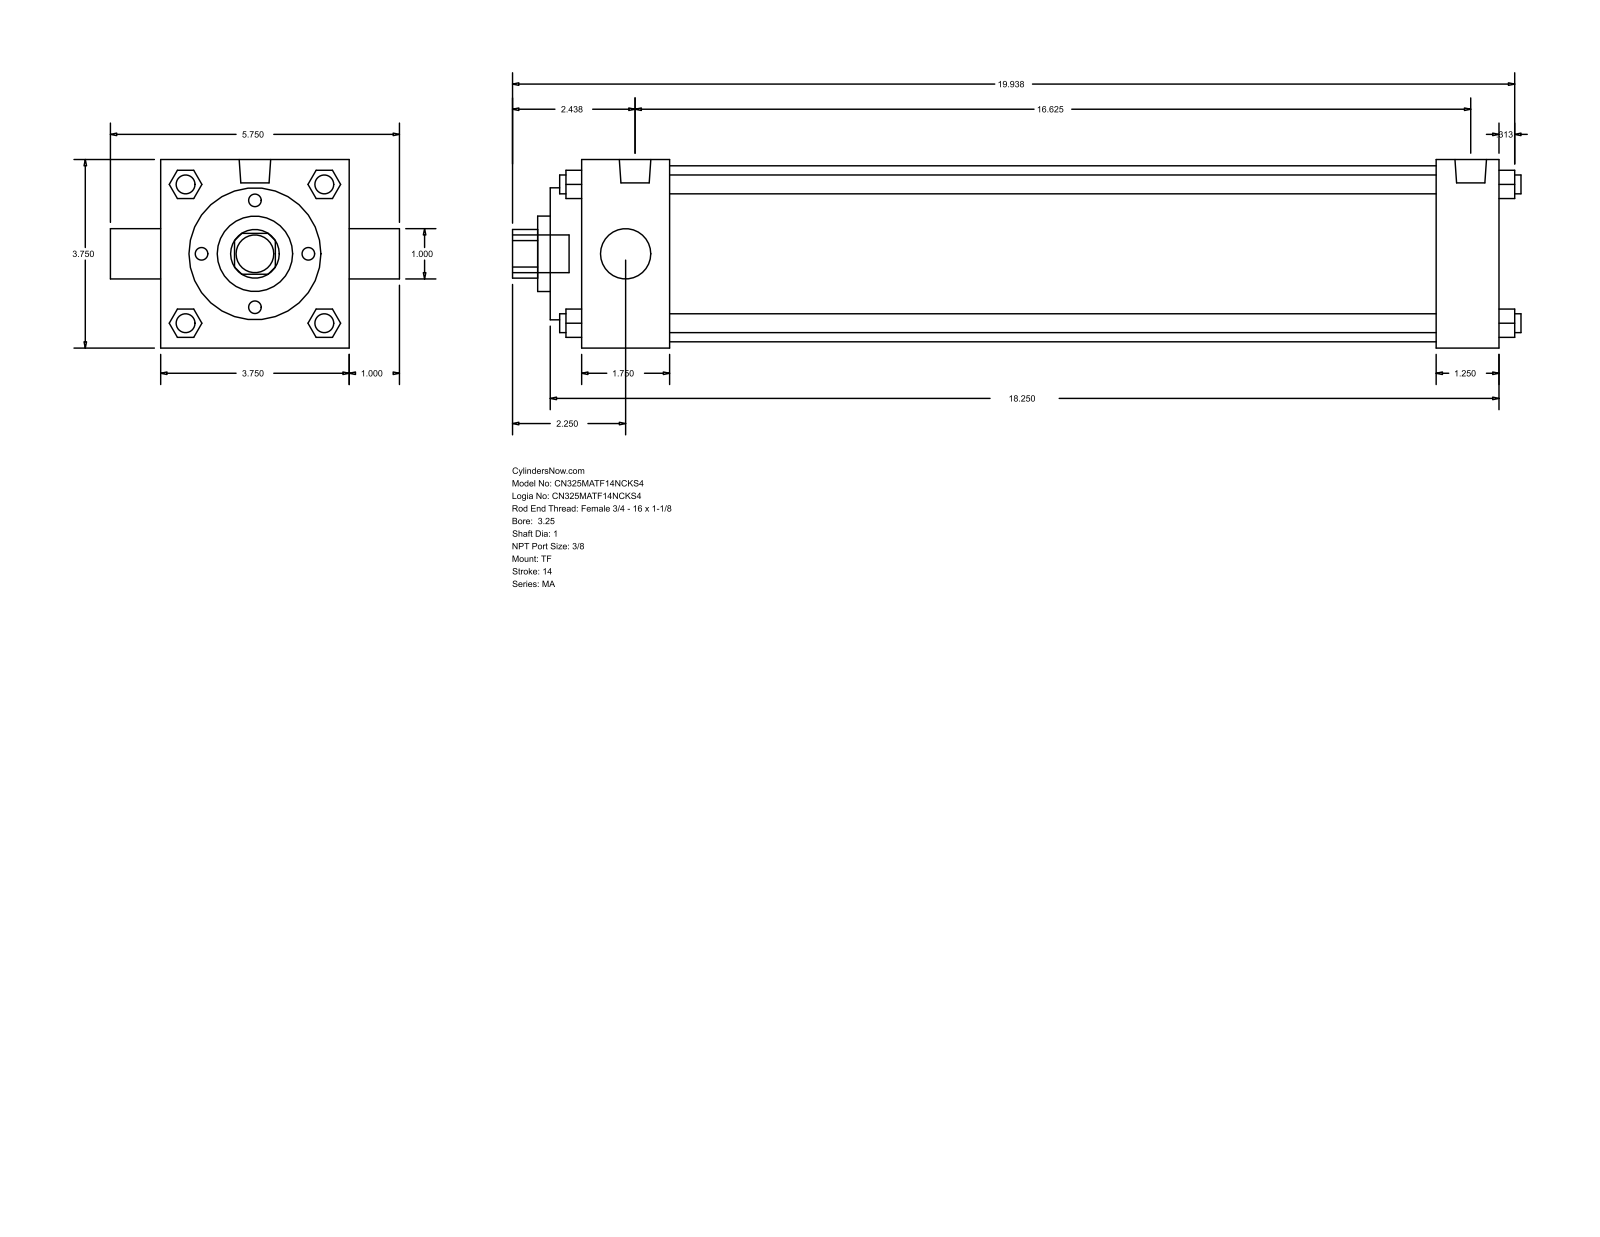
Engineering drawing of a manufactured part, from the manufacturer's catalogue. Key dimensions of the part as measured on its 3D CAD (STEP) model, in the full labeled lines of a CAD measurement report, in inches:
Part name (STEP PRODUCT): MA_TF__0325_1
STEP written by: GSSL Pune (CONFIG_CONTROL_DESIGN)
Units: inches
Bodies: 0 solids, 122 faces (93 planar, 29 cylindrical, 0 other)
Overall size (bounding box): 20.063 × 5.75 × 3.75
Round holes (diameter × count): ⌀1 ×2, ⌀1.5 ×1, ⌀2.625 ×1, ⌀3.5 ×1
Round bosses / shafts (diameter × count): ⌀0.375 ×4, ⌀0.437 ×3, ⌀0.627 ×2, ⌀0.75 ×1
Partial cylindrical surfaces — rounded edges, fillets, slot ends (radius × count): R0.484 ×1
Main face-to-face distances: 3.75, 18.25, 0.625, 1.75, 17, 15.25, 16.5, 1.25, 2.375, 17.625
